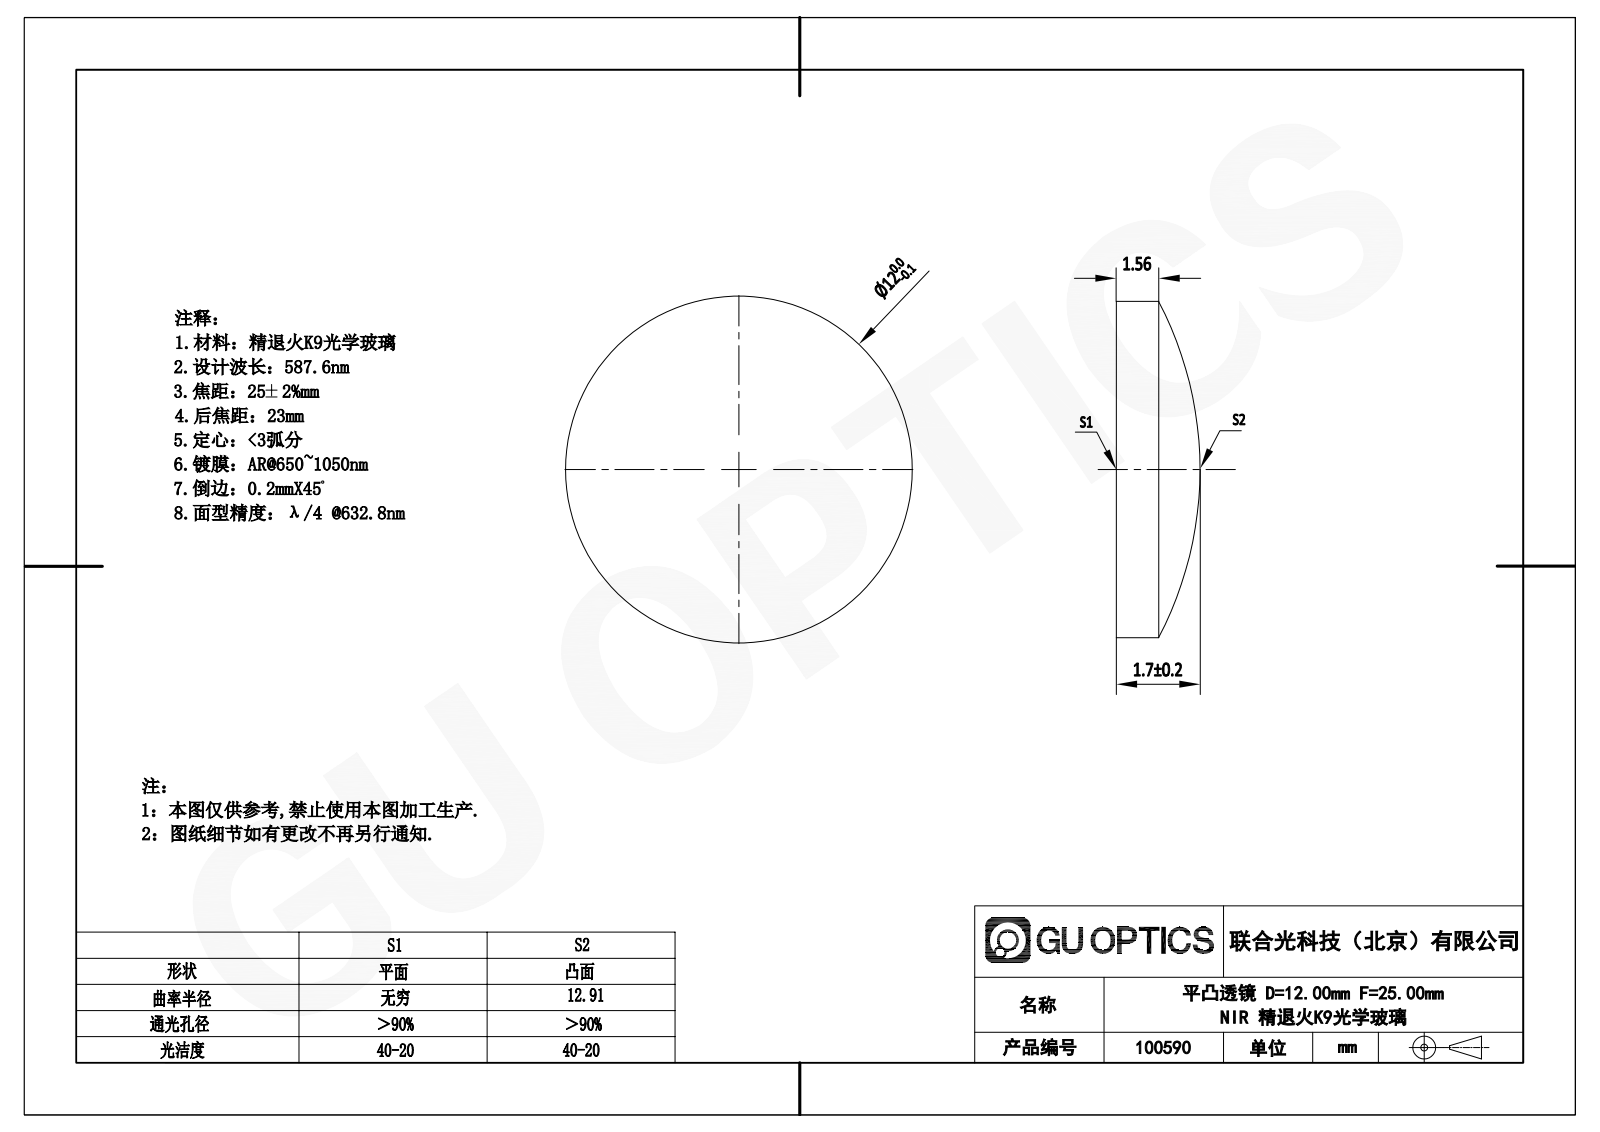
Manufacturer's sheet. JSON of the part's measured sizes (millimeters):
{"part_name": "100590", "step_written_by": "SolidWorks 2020 (CONFIG_CONTROL_DESIGN)", "units": "millimeters", "bodies": {"solids": 1, "faces": 5, "planar": 1, "cylindrical": 2, "other": 2}, "overall_size": [12, 12, 3], "volume_mm3": 257, "surface_area_mm2": 290, "round_bosses_or_shafts": [[12, 1]]}
